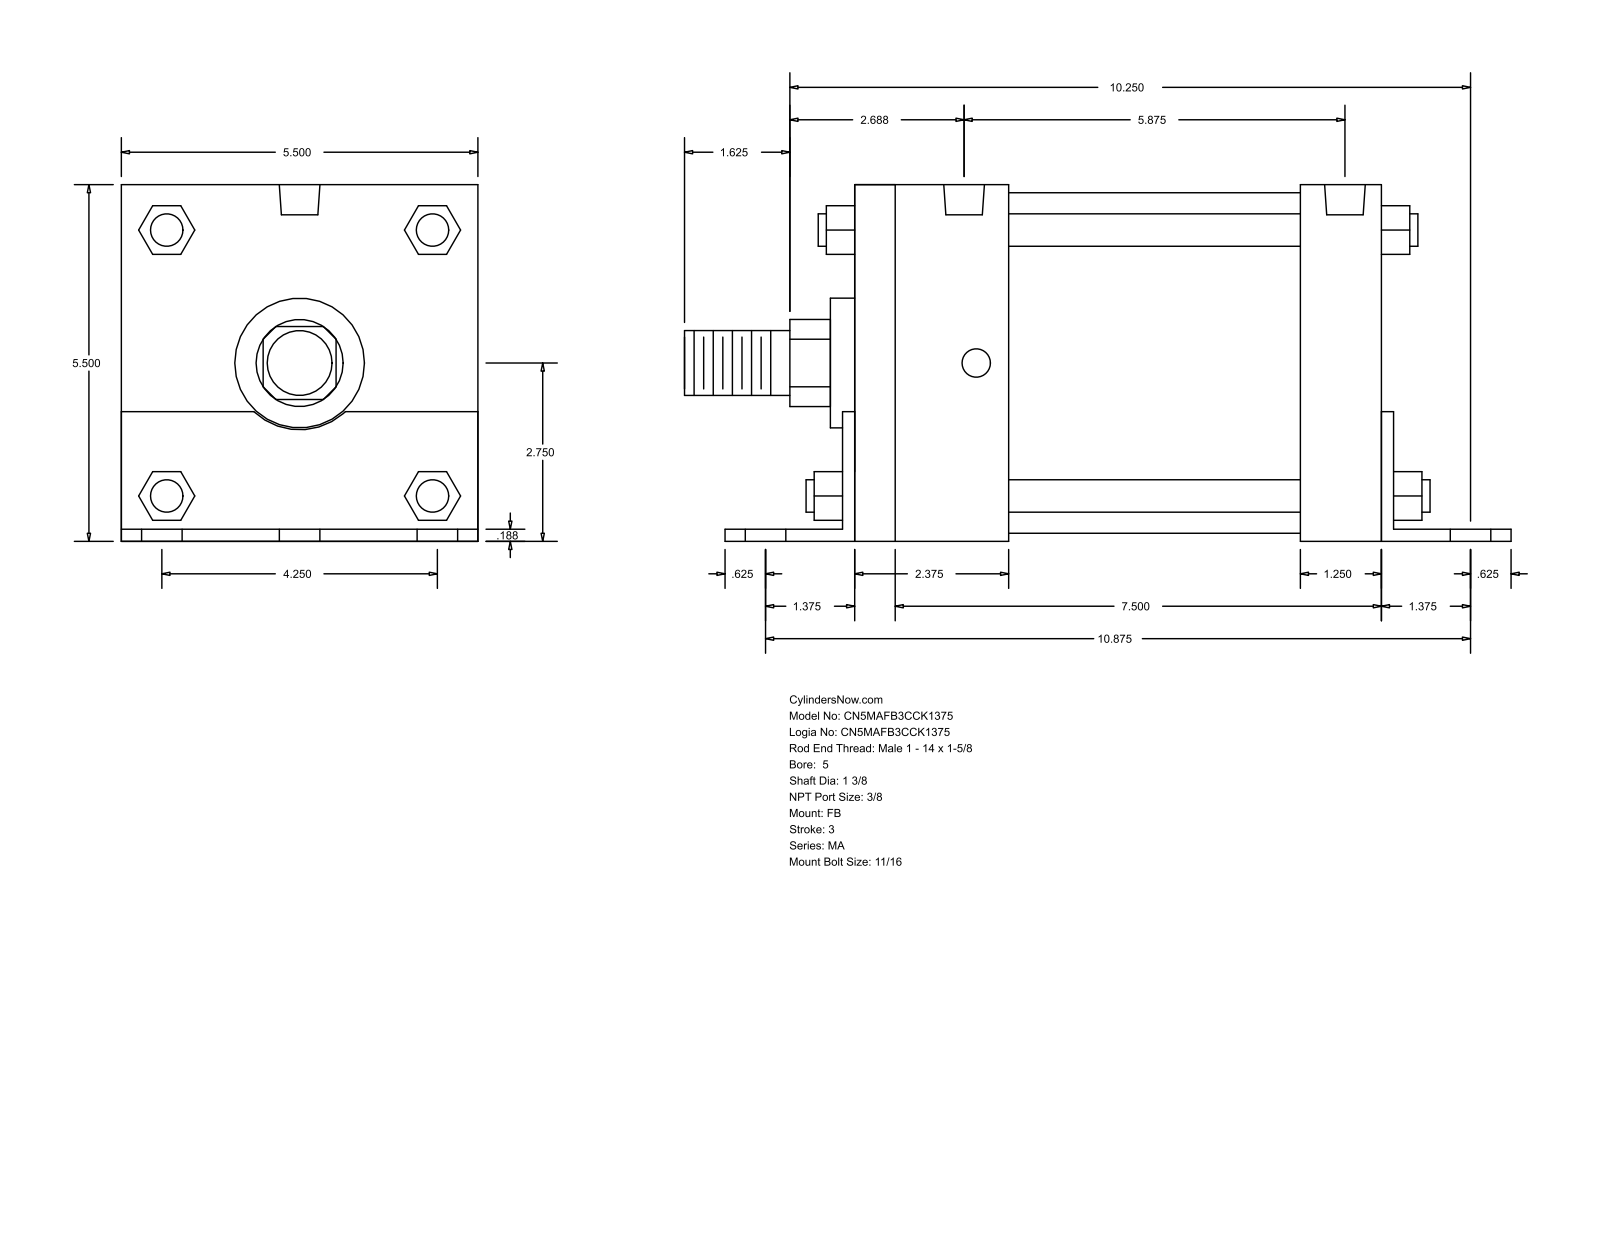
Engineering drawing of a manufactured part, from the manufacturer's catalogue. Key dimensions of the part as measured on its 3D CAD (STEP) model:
Part name (STEP PRODUCT): MA_FB__0500_1.375
STEP written by: GSSL Pune (CONFIG_CONTROL_DESIGN)
Units: millimetres
Bodies: 0 solids, 140 faces (105 planar, 35 cylindrical, 0 other)
Overall size (bounding box): 323.85 × 139.75 × 139.7
Round holes (diameter × count): ⌀17.46 ×6, ⌀11.11 ×4, ⌀15.93 ×2
Round bosses / shafts (diameter × count): ⌀12.7 ×4, ⌀133.35 ×1, ⌀50.8 ×1, ⌀34.92 ×1, ⌀25.4 ×1
Partial cylindrical surfaces — rounded edges, fillets, slot ends (radius × count): R17.06 ×1, R26.16 ×1
Main face-to-face distances: 139.7, 4.76, 139.75, 211.14, 4.71, 134.99, 206.38, 215.9, 31.75, 36.51
Hole centre spacings: 53.98, 281.45, 276.23, 4.77, 73.04, 76.34, 94.68, 98.64
